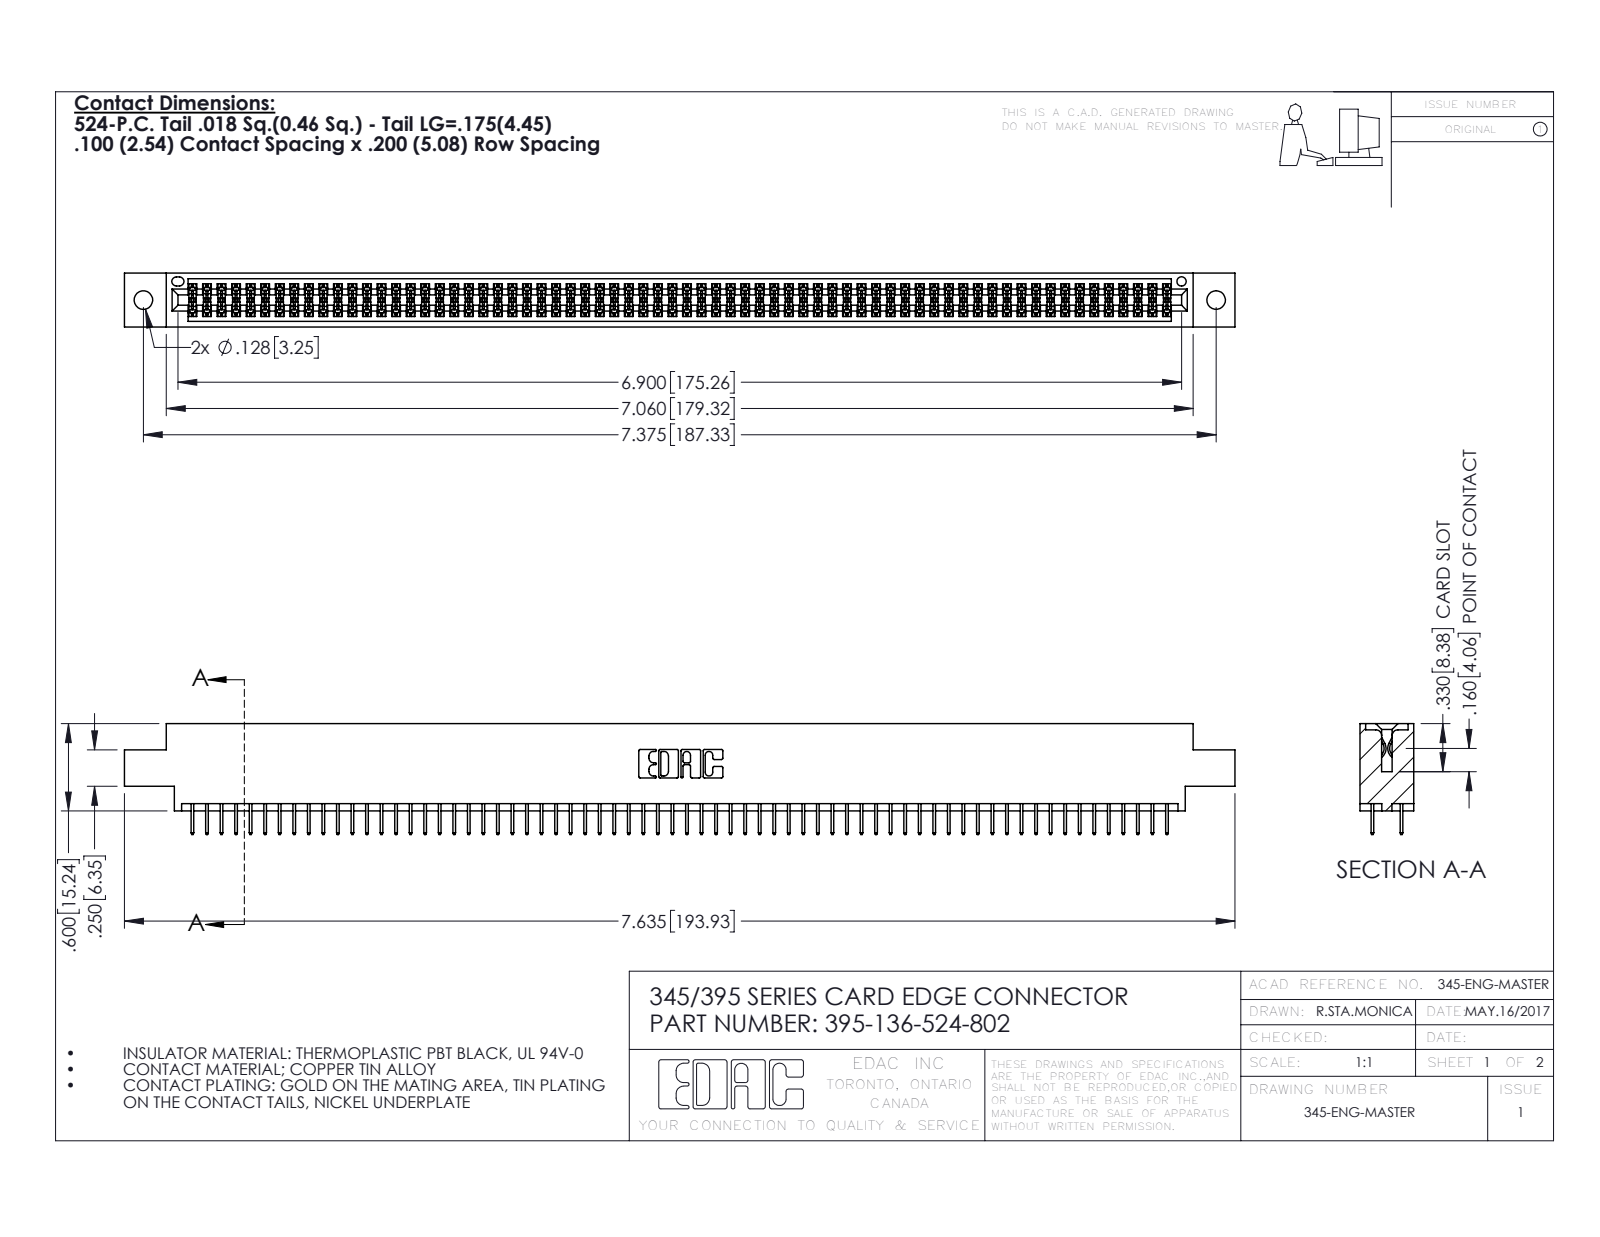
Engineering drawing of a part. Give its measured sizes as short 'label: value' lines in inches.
name: 395-136-524-802; 345 Part_0.170 Offset - 0.128 Dia; 345-292-001_345-293-124
written by: SolidWorks 2016 (CONFIG_CONTROL_DESIGN)
unit: in
bodies: 137 solids, 7474 faces (5388 planar, 2086 cylindrical, 0 other)
size: 7.635 × 0.762 × 0.37
volume: 1.143 in³; area: 42.64 in²
holes: 2× ⌀0.128, 1× ⌀0.064
rounds: 204× R0.006, 22× R0.01, 6× R0.007, 6× R0.031, 3× R0.026, 2× R0.014, 2× R0.019, 2× R0.022
face distances: 0.072, 0.298, 0.37, 0.2, 0.098, 0.272, 0.025, 0.225, 0.072, 0.175
hole spacings: 0.27, 7.139, 7.375
